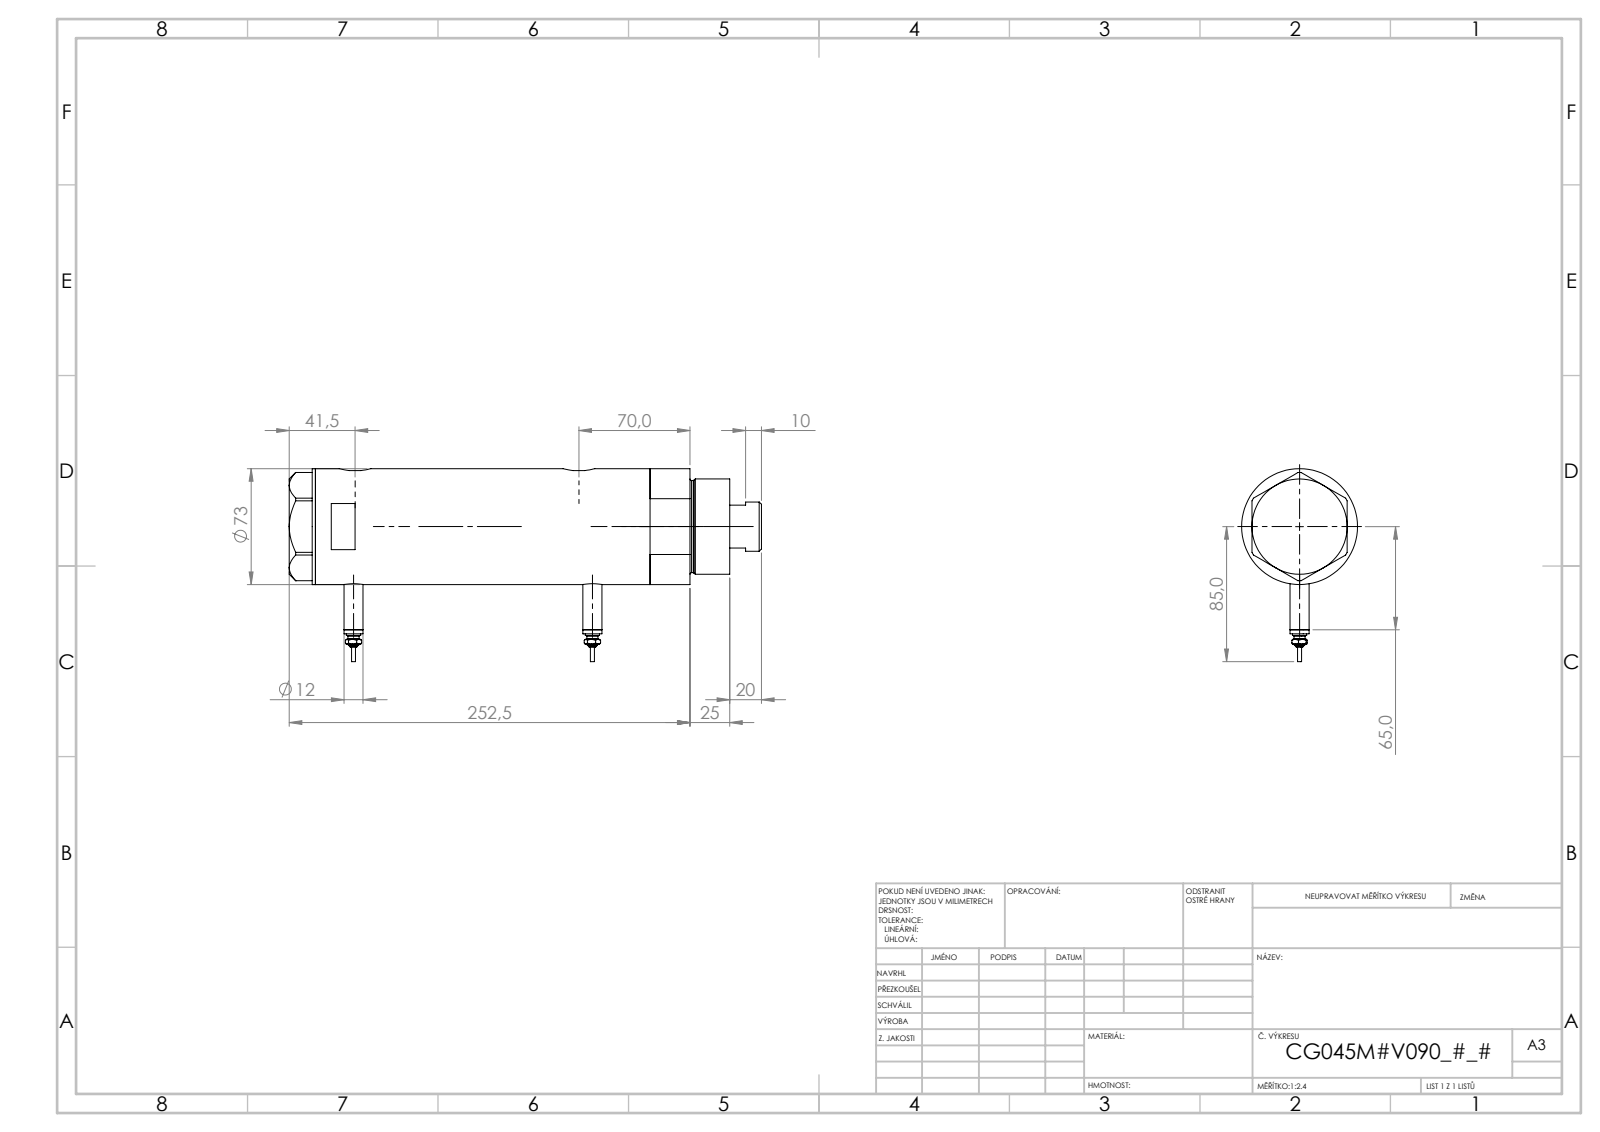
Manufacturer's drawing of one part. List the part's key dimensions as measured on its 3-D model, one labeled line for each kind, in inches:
Part name (STEP PRODUCT): V270CG_BACK; V270CG_FRONT; Switch; V270CG_VC (+1 more)
STEP written by: SolidWorks 2019 (CONFIG_CONTROL_DESIGN)
Units: inches
Bodies: 6 solids, 212 faces (77 planar, 71 cylindrical, 64 other)
Overall size (bounding box): 11.713 × 4.783 × 2.874
Volume: 64.01 in³ · Surface area: 268.4 in²
Round holes (diameter × count): ⌀0.492 ×2, ⌀0.518 ×2, ⌀0.413 ×1, ⌀1.26 ×1, ⌀1.319 ×1, ⌀1.772 ×1, ⌀1.89 ×1, ⌀2.52 ×1
Round bosses / shafts (diameter × count): ⌀0.472 ×2, ⌀0.354 ×2, ⌀0.276 ×2, ⌀0.177 ×2, ⌀0.098 ×2, ⌀2.874 ×1, ⌀2.362 ×1, ⌀2.283 ×1
Partial cylindrical surfaces — rounded edges, fillets, slot ends (radius × count): R0.394 ×2
Main face-to-face distances: 6.535, 1.024, 5.512, 0.65, 1.673, 7.185, 0.079, 10.276, 10.925, 9.252
Hole centre spacings: 0.039, 0.335, 5.551, 5.591, 5.886, 5.925
